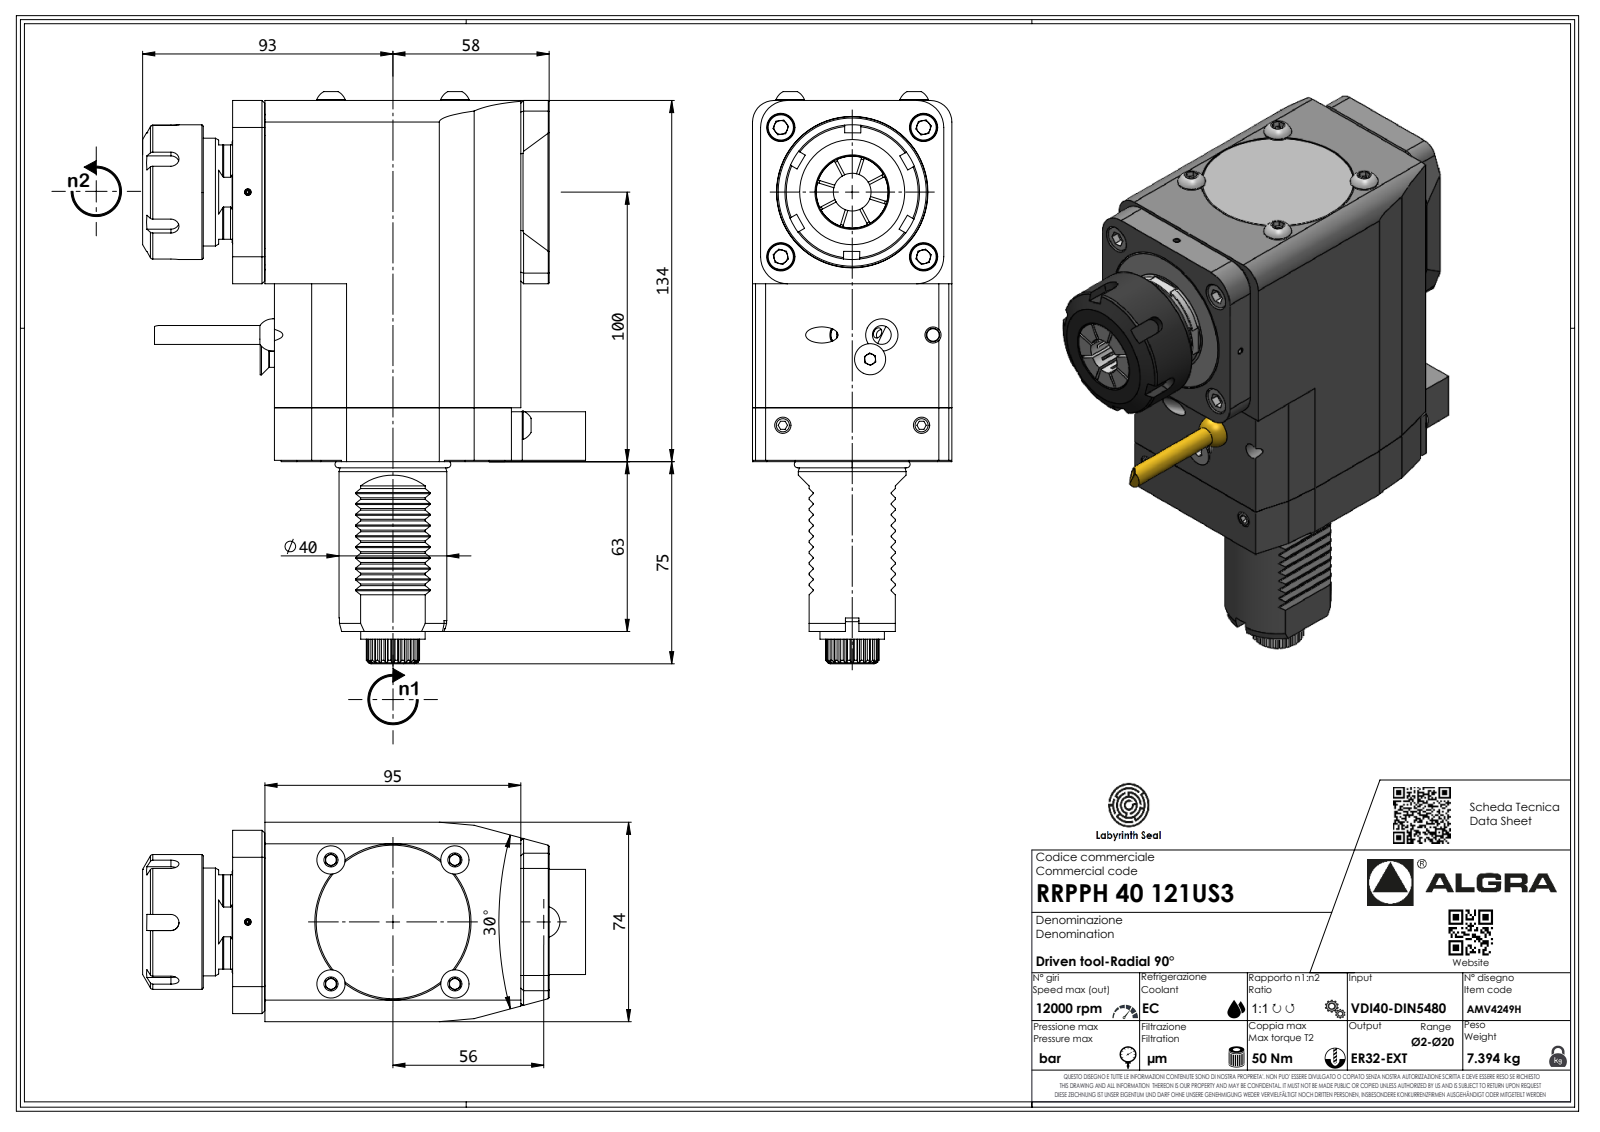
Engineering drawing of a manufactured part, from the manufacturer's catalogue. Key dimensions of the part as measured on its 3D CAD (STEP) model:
Part name (STEP PRODUCT): RRPPH40121US3
STEP written by: SolidWorks 2023 (AUTOMOTIVE_DESIGN)
Units: millimetres
Bodies: 4 solids, 711 faces (473 planar, 119 cylindrical, 119 other)
Overall size (bounding box): 209 × 164.41 × 74
Volume: 1 178 000 mm³ · Surface area: 95 716 mm²
Round holes (diameter × count): ⌀14 ×4, ⌀2.1 ×1, ⌀30.4 ×1
Round bosses / shafts (diameter × count): ⌀40 ×2, ⌀50 ×1, ⌀38.7 ×1, ⌀28.17 ×1, ⌀23.9 ×1, ⌀6.37 ×1, ⌀1.7 ×1
Partial cylindrical surfaces — rounded edges, fillets, slot ends (radius × count): R0.3 ×20, R0.33 ×7, R0.52 ×7, R3 ×7, R3.7 ×7, R6 ×4, R10 ×4, R8 ×2
Main face-to-face distances: 74, 91.5, 10.5, 3.5, 102, 117.5, 15.5, 107, 134, 68
Hole centre spacings: 41.87, 54, 64, 83.74
